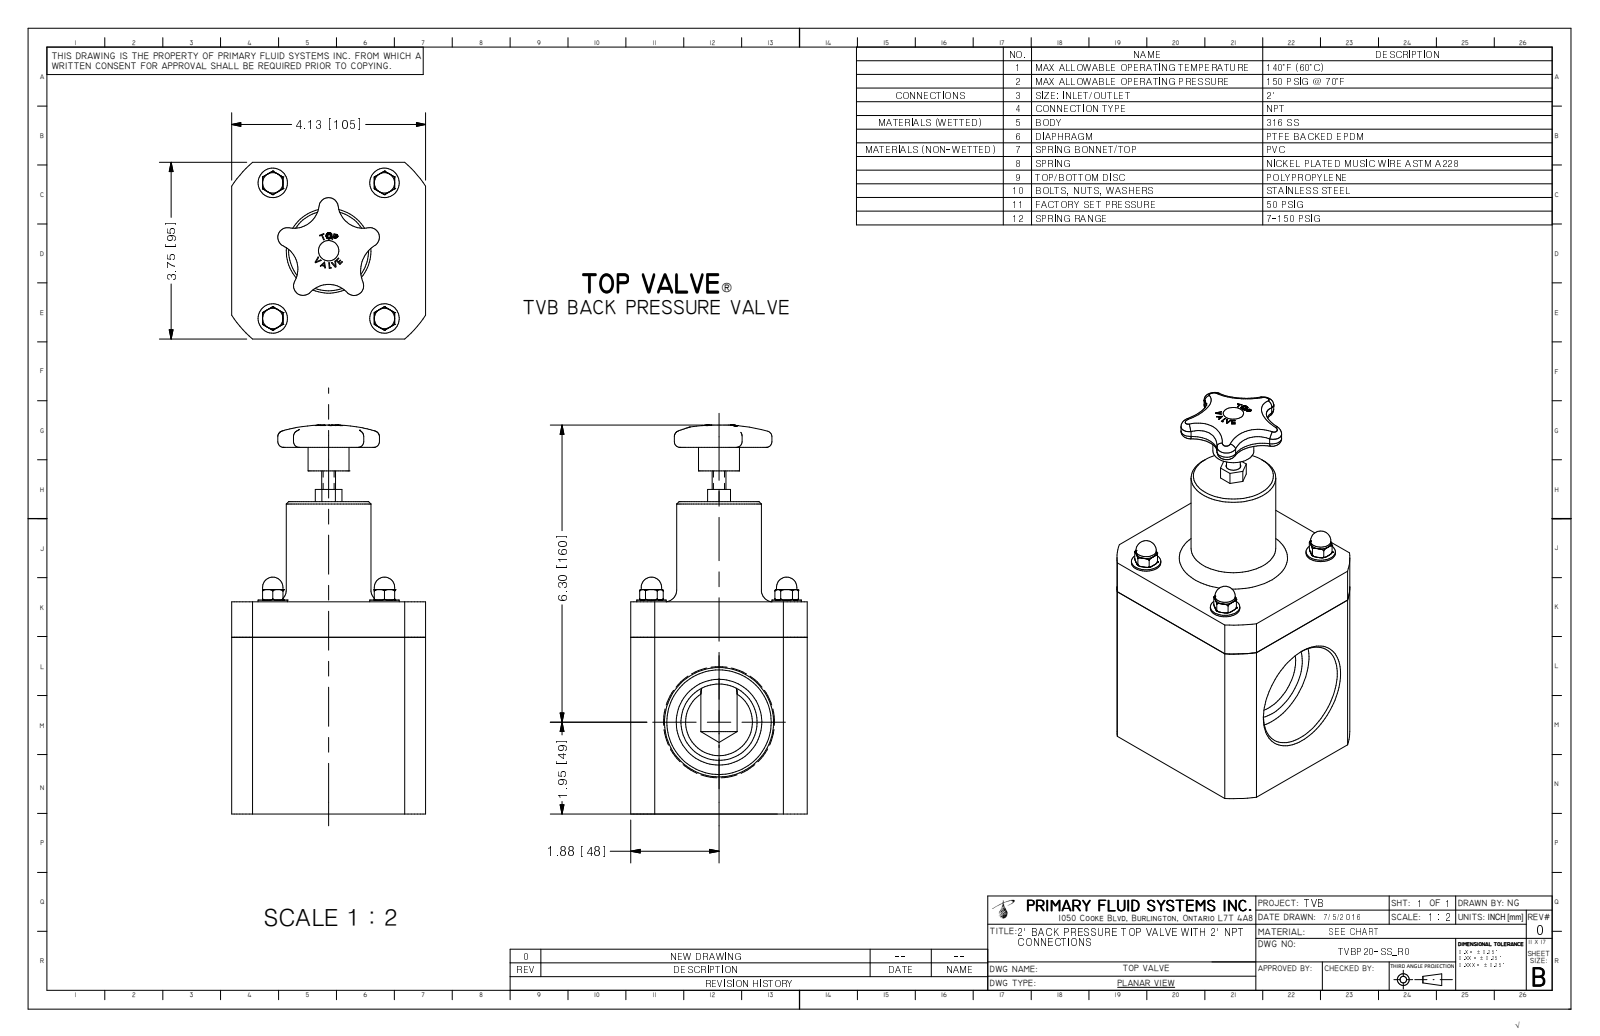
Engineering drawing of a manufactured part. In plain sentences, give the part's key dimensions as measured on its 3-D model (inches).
The part is named "TVBP20-SS-R0". Its 3-D file was written by "Autodesk Inventor 2009 (AUTOMOTIVE_DESIGN)". It is 1 solid with 337 faces: 144 planar, 45 cylindrical and 148 other. Overall it measures 8.25 by 4.125 by 3.75 inches. Its volume is 67.72 cubic inches and its surface area 135.7 square inches. Round holes: 4 of diameter 0.175, 1 of diameter 2.219. Round bosses or shafts: 4 of diameter 0.625, 4 of diameter 0.433, 4 of diameter 0.375, 1 of diameter 1.8, 1 of diameter 0.87, 1 of diameter 0.293. Partial cylindrical surfaces (rounded edges, fillets, slot ends): 5 of radius 0.085, 5 of radius 0.205, 4 of radius 0.536, 4 of radius 0.656, 1 of radius 0.625, 1 of radius 0.745, 1 of radius 2.475. The main face-to-face distances are 3.75, 4.5, 4.125, 0.9, 3.225, 2.325, 6.625, 2.125, 0.433, 4.536. The hole center spacings are 2.375, 2.875, 3.729.
